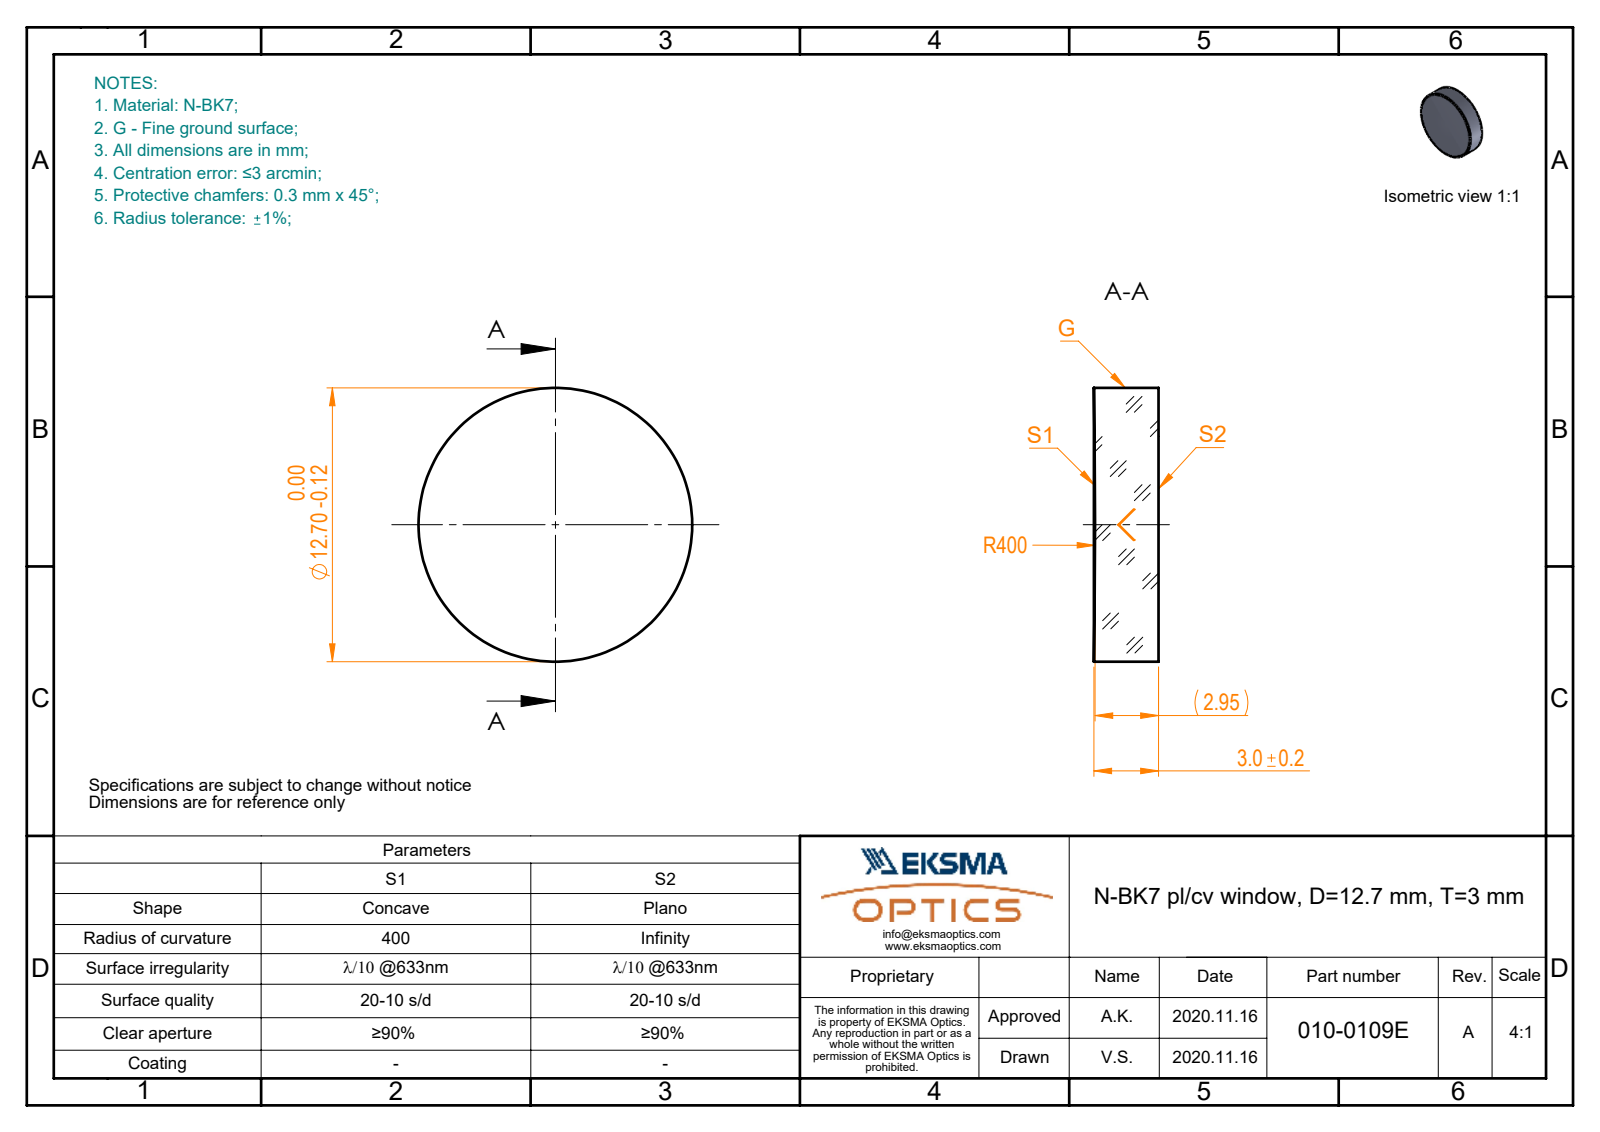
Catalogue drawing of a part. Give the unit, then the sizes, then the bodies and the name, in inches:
Units: inches
Overall size (bounding box): 0.5 × 0.5 × 0.118
Round bosses / shafts (diameter × count): ⌀0.5 ×1
Volume: 0.023 in³ · Surface area: 0.578 in²
Bodies: 1 solid, 5 faces (1 planar, 2 cylindrical, 2 other)
Part name (STEP PRODUCT): 010-0109E_N-BK7_PCV_window
STEP written by: SolidWorks 2019 (CONFIG_CONTROL_DESIGN)
